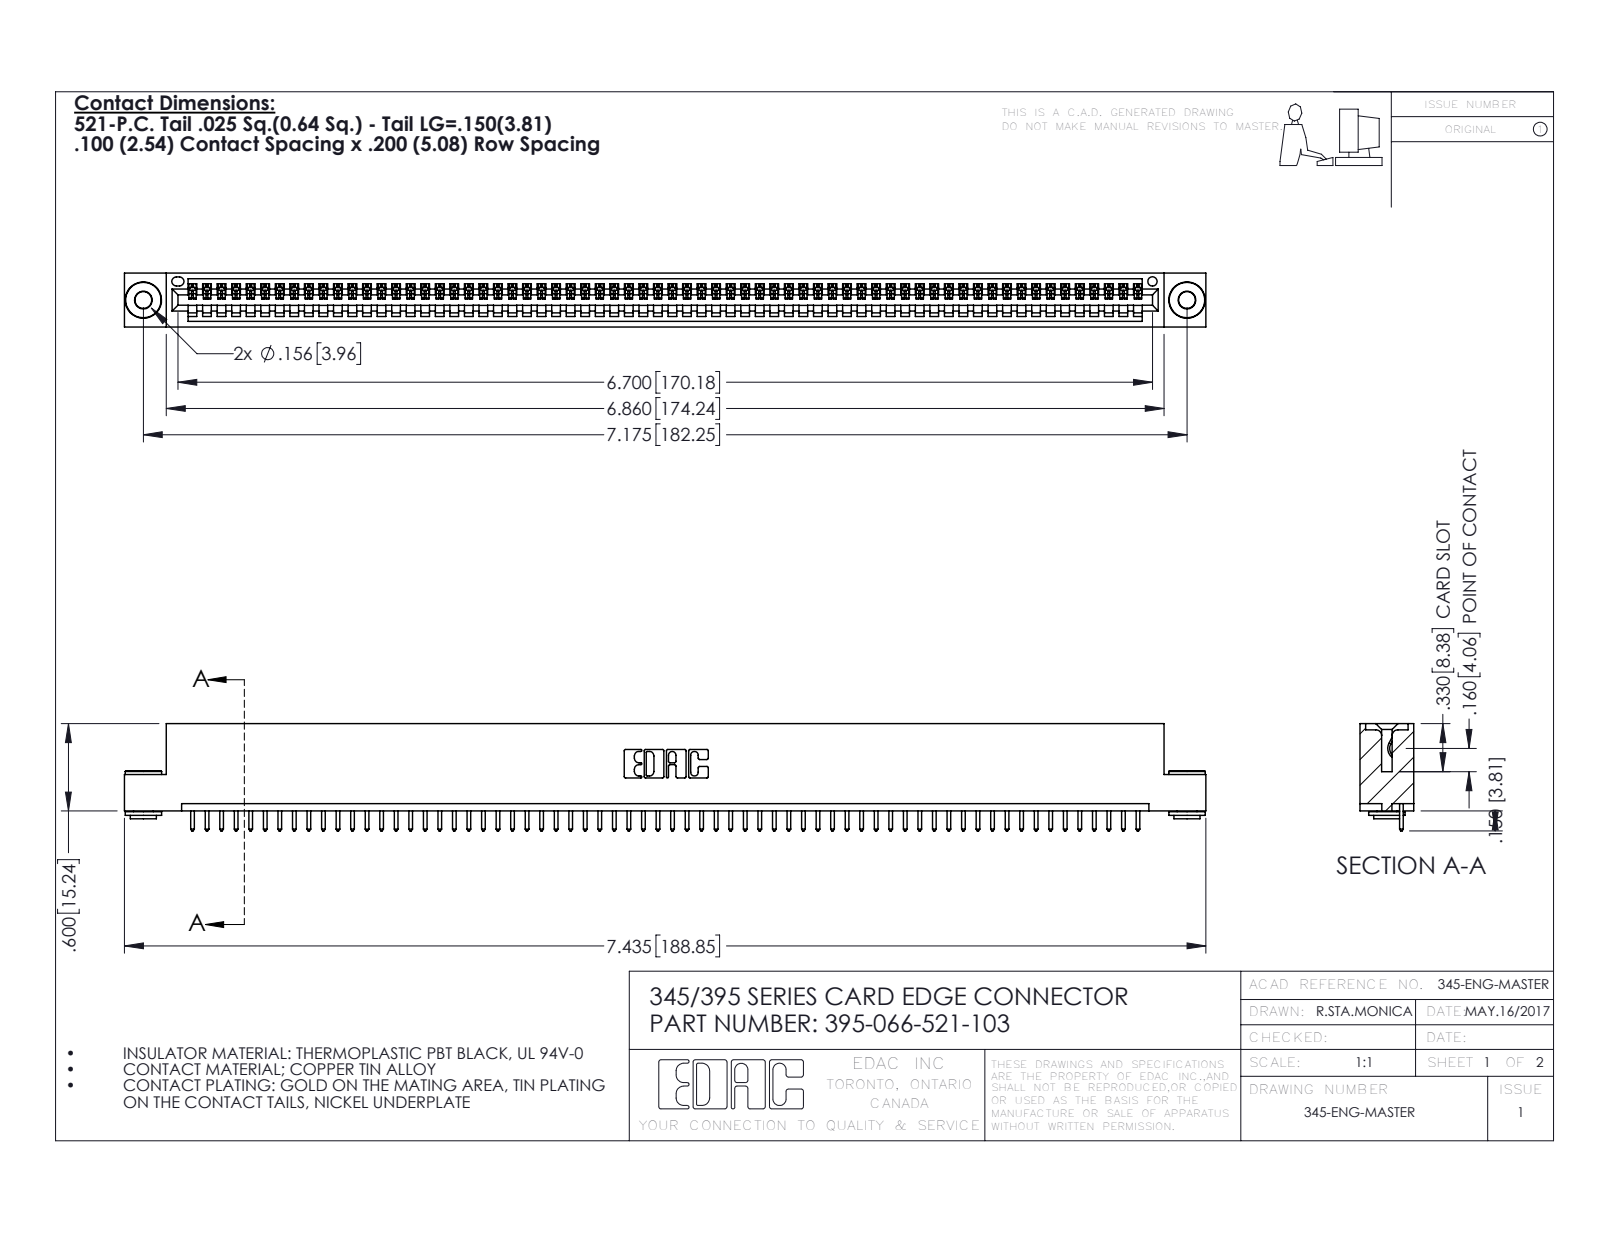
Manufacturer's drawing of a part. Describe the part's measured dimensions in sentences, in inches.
The part is named "345 Part_Flush Mounting Lugs - 0.156 Dia-TH; 345-292-001_345-293-121; 395-066-521-103; 345-250-002_345-250-002-102". Its 3-D file was written by "SolidWorks 2016 (CONFIG_CONTROL_DESIGN)". It is 69 solids with 3992 faces: 2730 planar, 1254 cylindrical and 8 other. Overall it measures 7.435 by 0.737 by 0.37 inches. Its volume is 1.096 cubic inches and its surface area 36.7 square inches. Round holes: 2 of diameter 0.116, 2 of diameter 0.156, 1 of diameter 0.064. Round bosses or shafts: 2 of diameter 0.25, 2 of diameter 0.18, 2 of diameter 0.136. Partial cylindrical surfaces (rounded edges, fillets, slot ends): 132 of radius 0.006, 132 of radius 0.01, 22 of radius 0.01, 6 of radius 0.007, 6 of radius 0.031, 3 of radius 0.026, 2 of radius 0.031, 2 of radius 0.04. The main face-to-face distances are 0.072, 0.298, 0.37, 0.2, 0.025, 0.098, 0.272, 0.225, 0.149, 0.072. The hole center spacings are 0.27, 6.939, 7.175.
